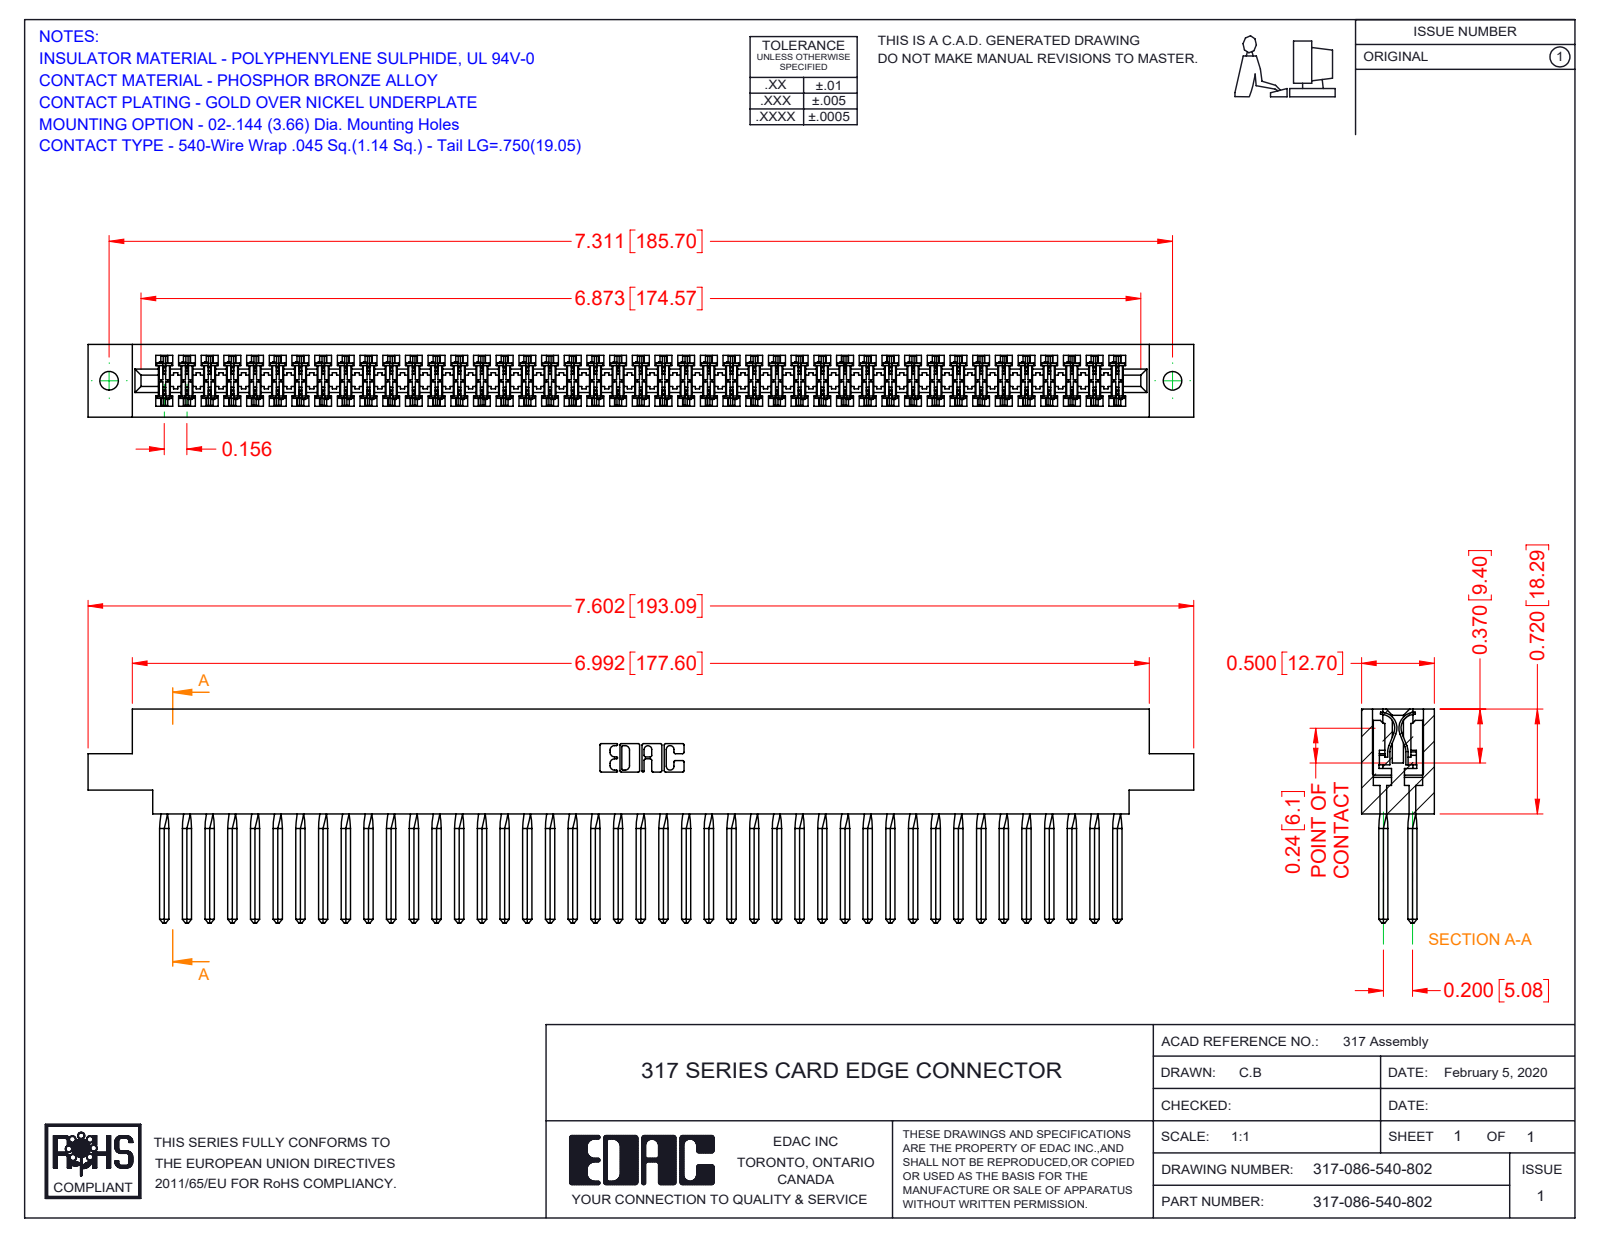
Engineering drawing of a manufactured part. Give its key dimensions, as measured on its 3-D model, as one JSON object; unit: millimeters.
{"part_name": "317-086-540-802; 317-290-001_540; 317 Part_.144 Dia", "step_written_by": "SolidWorks 2016 (CONFIG_CONTROL_DESIGN)", "units": "millimeters", "bodies": {"solids": 87, "faces": 7756, "planar": 6336, "cylindrical": 1076, "other": 344}, "overall_size": [193.1, 37.3, 12.7], "volume_mm3": 32400, "surface_area_mm2": 48080, "round_holes": [[3.3, 2]], "partial_cylinders_radius": [[0.4, 172], [0.3, 22], [0.2, 6], [0.8, 6], [0.7, 3], [2.4, 2], [2.5, 2], [2.8, 2]], "face_to_face_distances": [12.7, 1.9, 10.8, 8.9, 5, 2.4, 5.1, 2.9, 3.3, 1.2], "hole_center_spacings": [185.7]}
